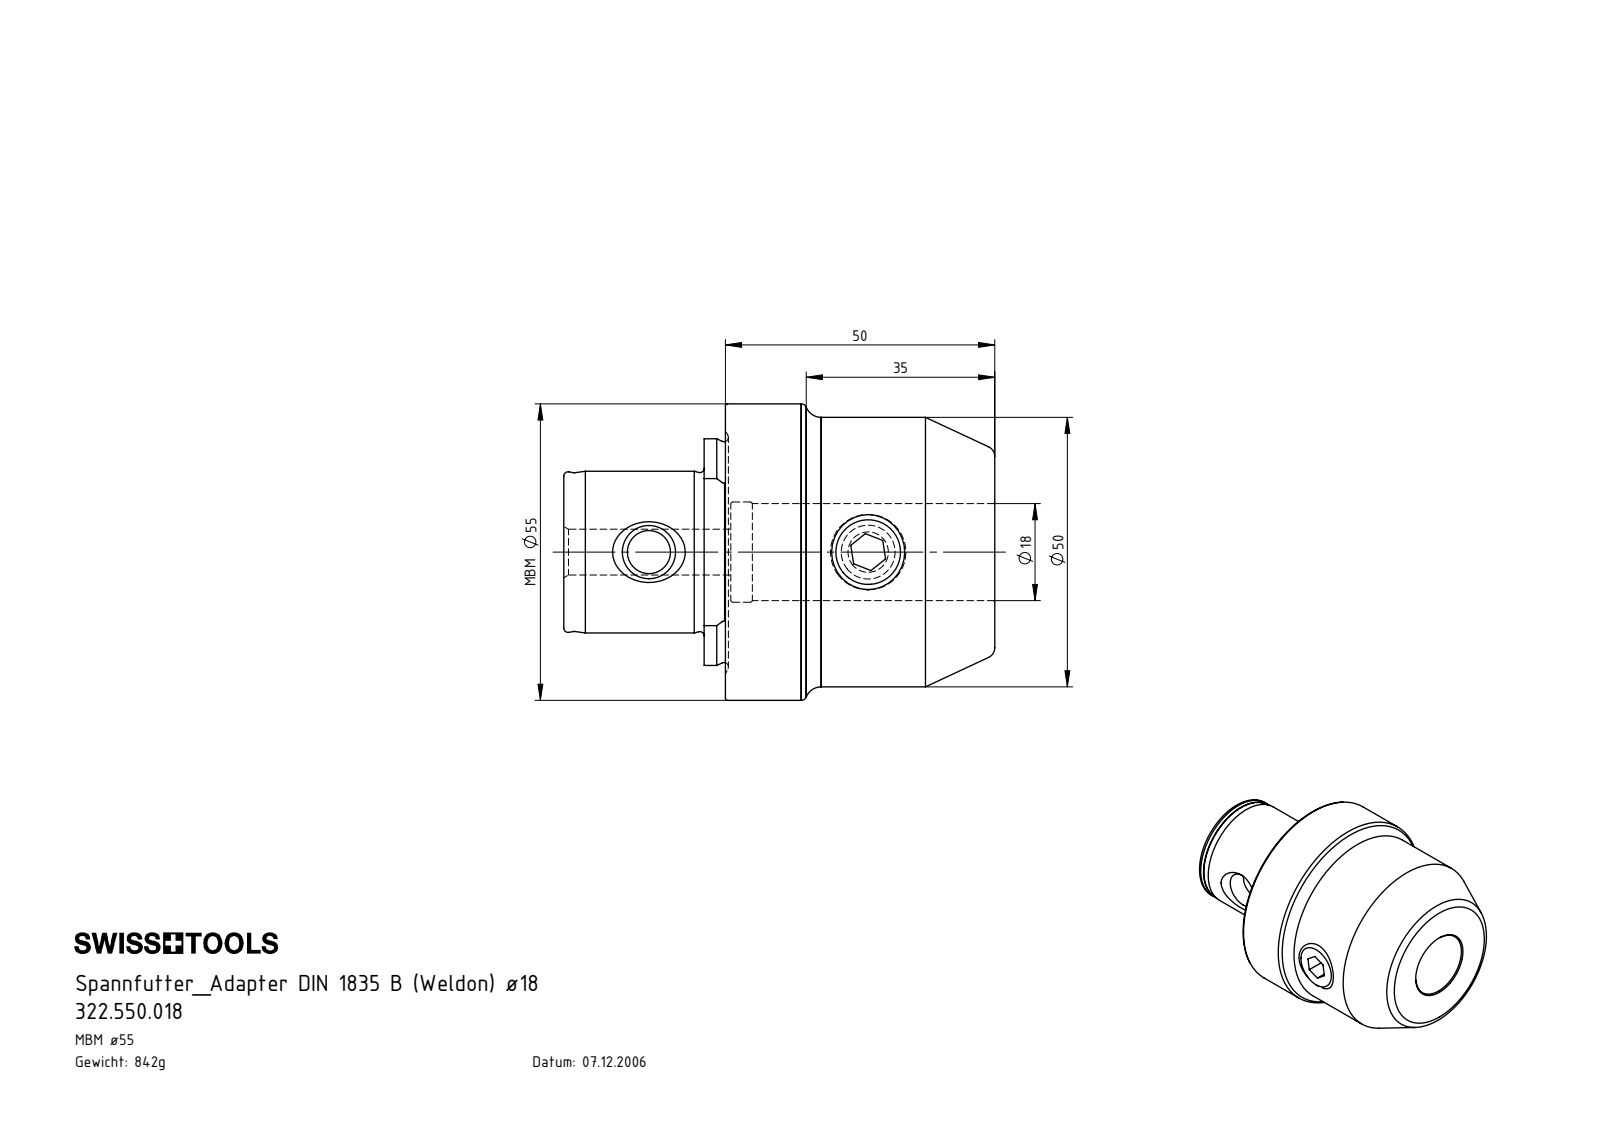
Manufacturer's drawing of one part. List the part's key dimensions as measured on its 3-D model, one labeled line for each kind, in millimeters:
Part name (STEP PRODUCT): W16-ER1.001.016; MB5.W18.K01.050; MB5-W18.K01.050_C
STEP written by: SolidWorks 2017 (AUTOMOTIVE_DESIGN)
Units: millimetres
Bodies: 2 solids, 55 faces (18 planar, 11 cylindrical, 26 other)
Overall size (bounding box): 80 × 55 × 55
Volume: 107 257 mm³ · Surface area: 19 804 mm²
Round holes (diameter × count): ⌀8 ×1, ⌀8.5 ×1, ⌀12 ×1, ⌀18 ×1, ⌀18.6 ×1
Round bosses / shafts (diameter × count): ⌀55 ×1, ⌀50 ×1, ⌀30 ×1, ⌀14 ×1
Partial cylindrical surfaces — rounded edges, fillets, slot ends (radius × count): R21.02 ×1
Main face-to-face distances: 50, 30, 80, 26.05, 3.95, 53.95, 1, 31, 4.95, 49
Hole centre spacings: 40.7
